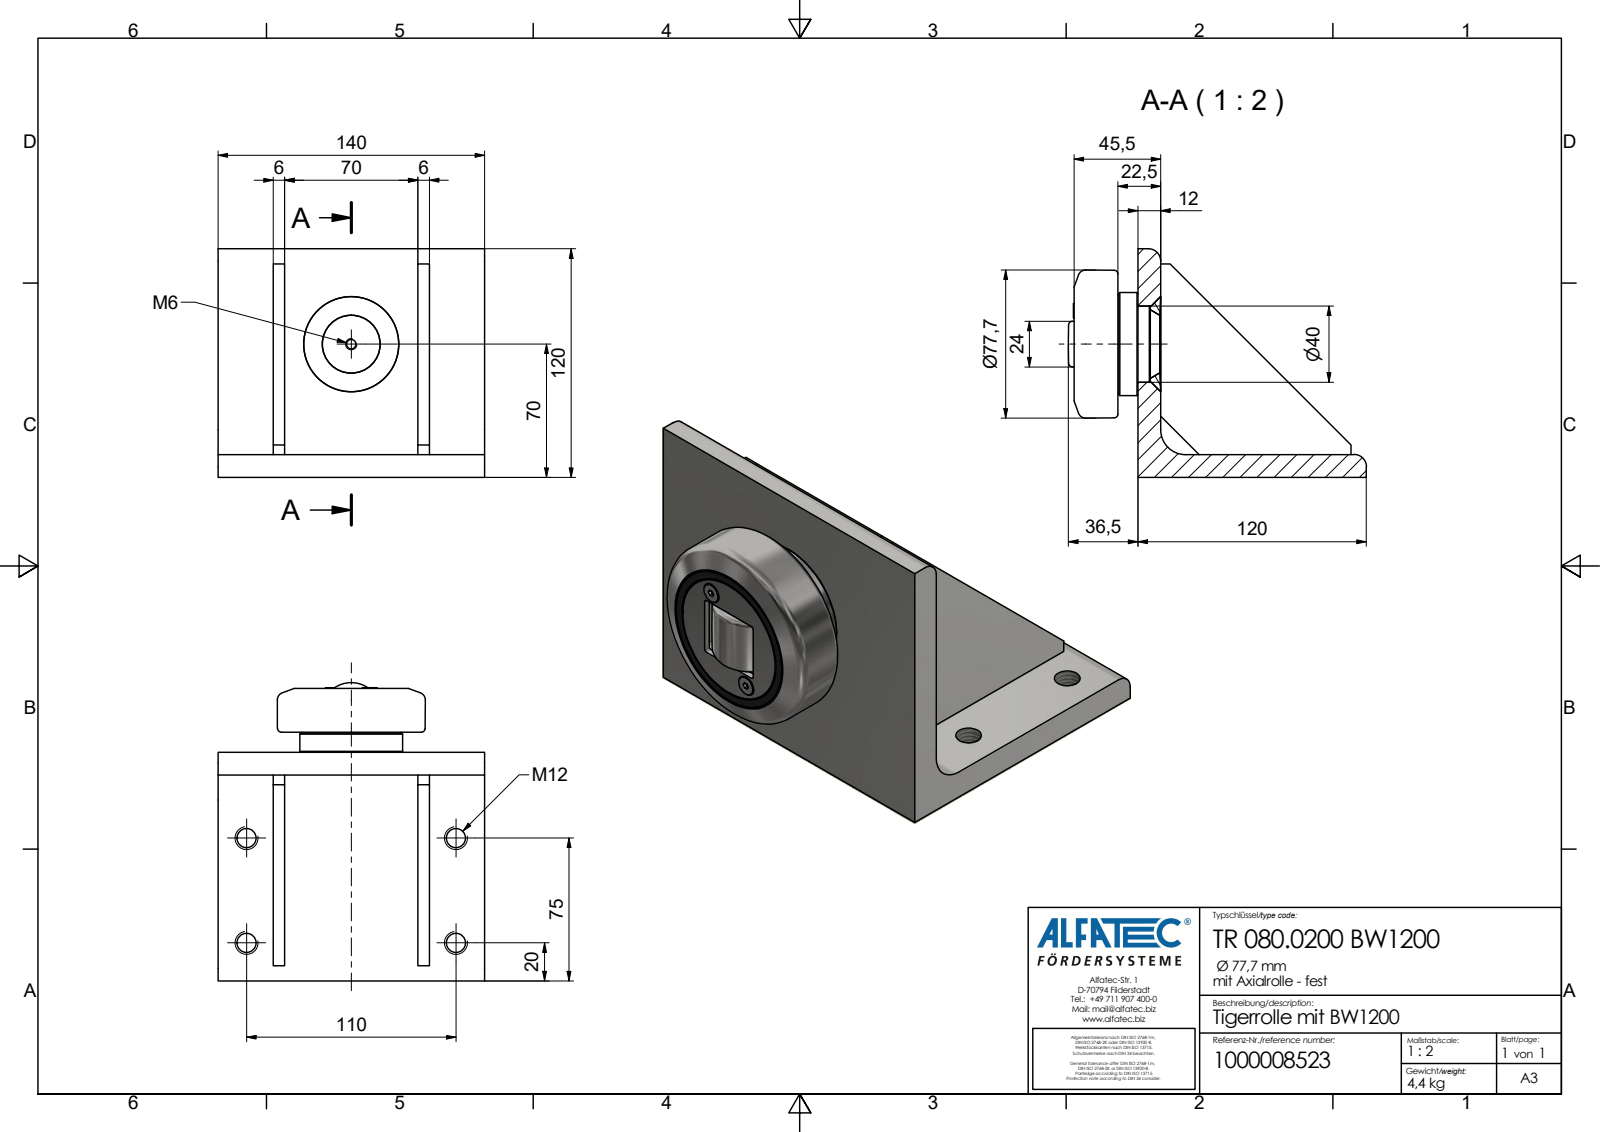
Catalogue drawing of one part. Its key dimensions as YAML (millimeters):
part_name: "TR 080.0200 BW1200_Kontur"
step_written_by: "Autodesk Inventor 2020 (AP242_MANAGED_MODEL_BASED_3D_ENGINEERING_MIM_LF)"
units: millimeters
bodies: {solids: 1, faces: 71, planar: 46, cylindrical: 15, other: 10}
overall_size: [156.5, 140, 120]
volume: 574189
surface_area: 105384
round_holes:
  - {diameter: 10.11, count: 4}
  - {diameter: 2.5, count: 1}
  - {diameter: 4.92, count: 1}
round_bosses_or_shafts:
  - {diameter: 7.8, count: 2}
  - {diameter: 54, count: 1}
  - {diameter: 52, count: 1}
partial_cylinders:
  - {radius: 6.5, count: 2}
  - {radius: 1.5, count: 1}
  - {radius: 13, count: 1}
  - {radius: 23, count: 1}
face_to_face_distances: [12, 76, 6, 35, 29, 105, 111, 82, 70, 140]
hole_center_spacings: [55, 110, 122.98]
